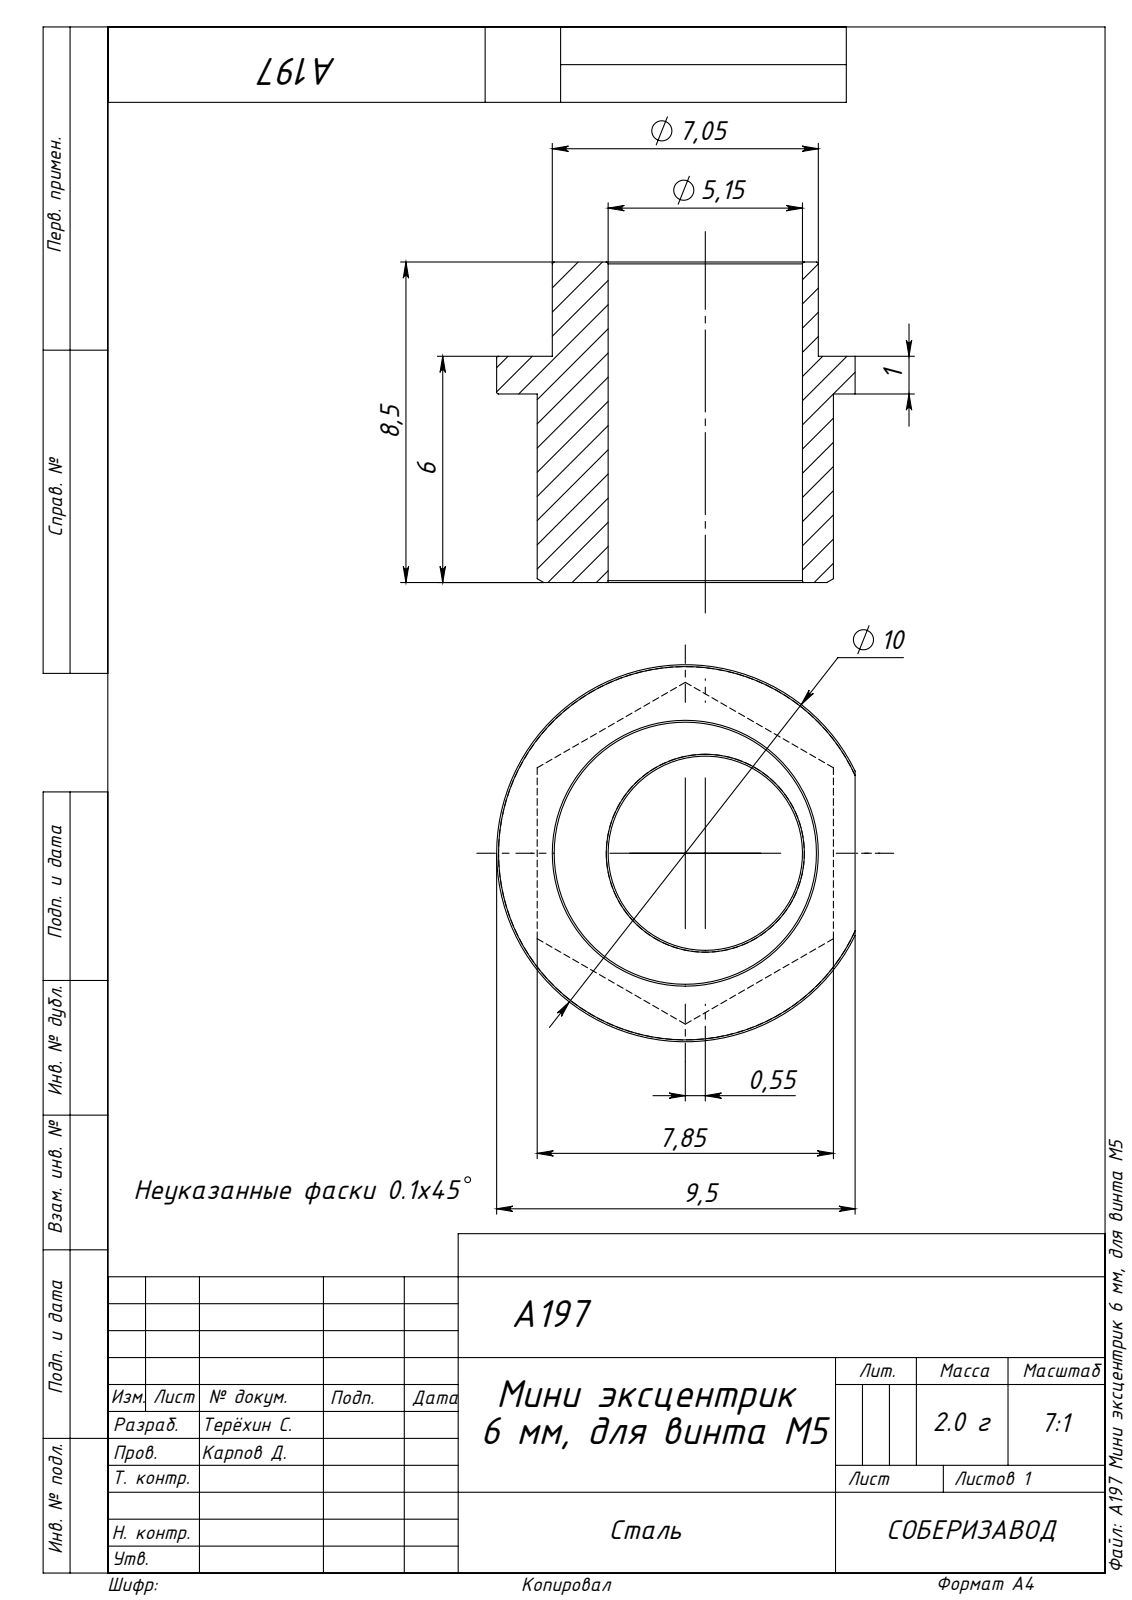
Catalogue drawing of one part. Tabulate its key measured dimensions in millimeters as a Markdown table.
| quantity | value |
| --- | --- |
| part name | A197 Мини эксцентрик 6 мм, для винта М5 |
| STEP written by | SolidWorks 2019 (AUTOMOTIVE_DESIGN) |
| units | millimeters |
| bodies | 1 solid, 32 faces (11 planar, 7 cylindrical, 14 other) |
| overall size | 10 × 9.5 × 8.5 |
| volume | 265 mm³ |
| surface area | 466 mm² |
| round holes (diameter × count) | 5.15 × 1 |
| round bosses / shafts (diameter × count) | 10 × 1, 7.1 × 1 |
| main face-to-face distances | 7.84, 6, 1, 5, 7.86, 2.5, 3.5, 8.5, 8.43, 0.57 |
